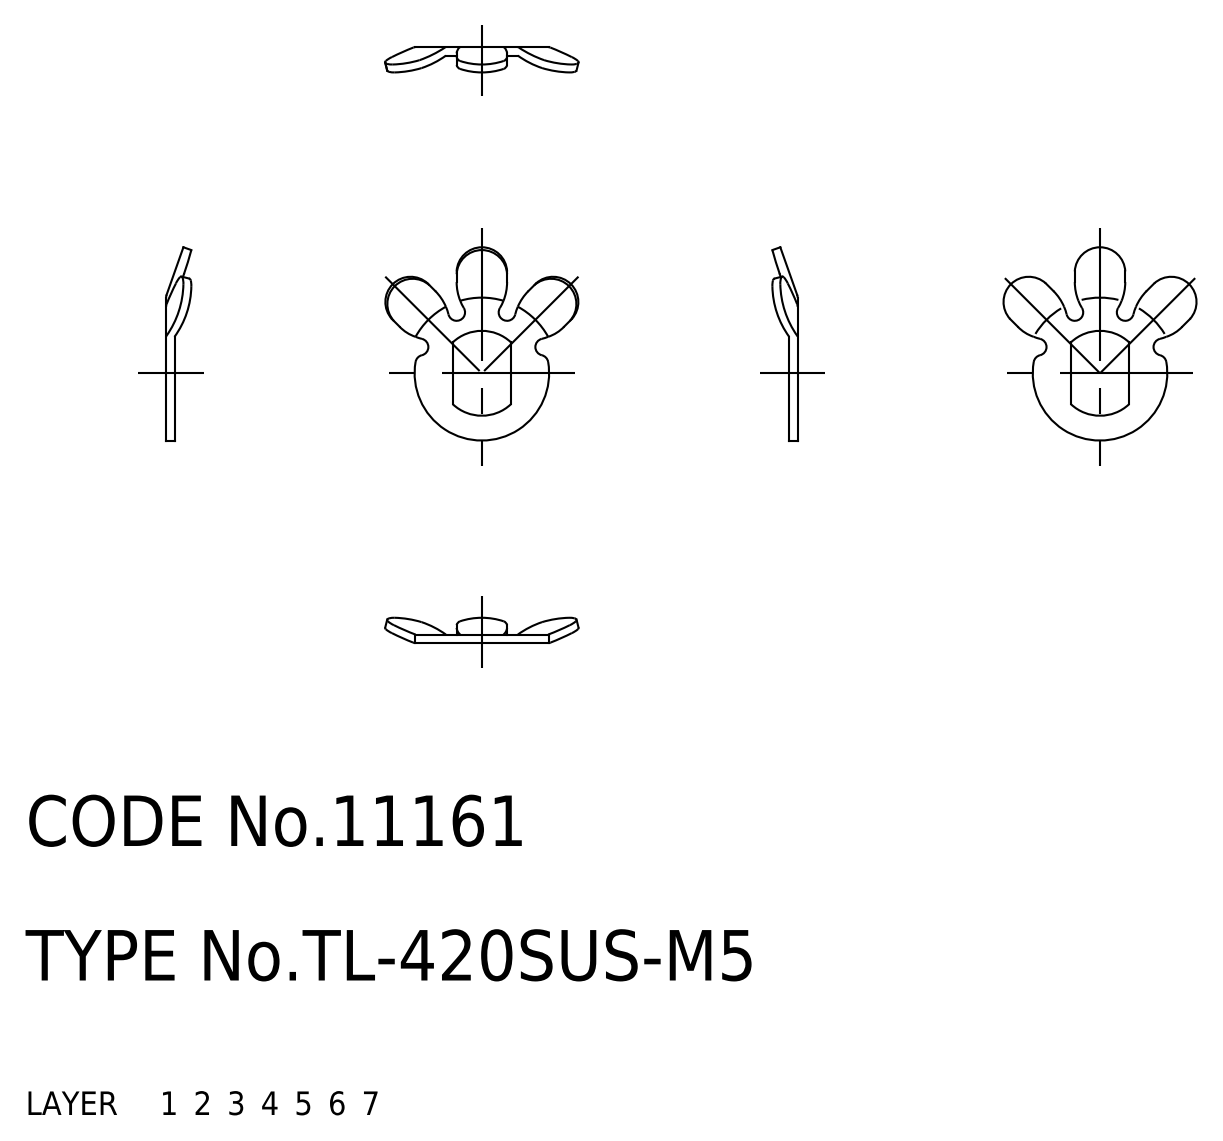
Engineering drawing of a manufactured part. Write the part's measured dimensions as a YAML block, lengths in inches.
part_name: "washer; TL_420SUS_M5"
step_written_by: "SolidWorks 2015 (AUTOMOTIVE_DESIGN)"
units: inches
bodies: {solids: 1, faces: 45, planar: 10, cylindrical: 26, other: 9}
overall_size: [0.453, 0.452, 0.059]
volume: 0.002
surface_area: 0.239
partial_cylinders:
  - {radius: 0.02, count: 6}
  - {radius: 0.118, count: 6}
  - {radius: 0.059, count: 3}
  - {radius: 0.099, count: 1}
  - {radius: 0.157, count: 1}
face_to_face_distances: [0.02, 0.136, 0.118, 0.127]
